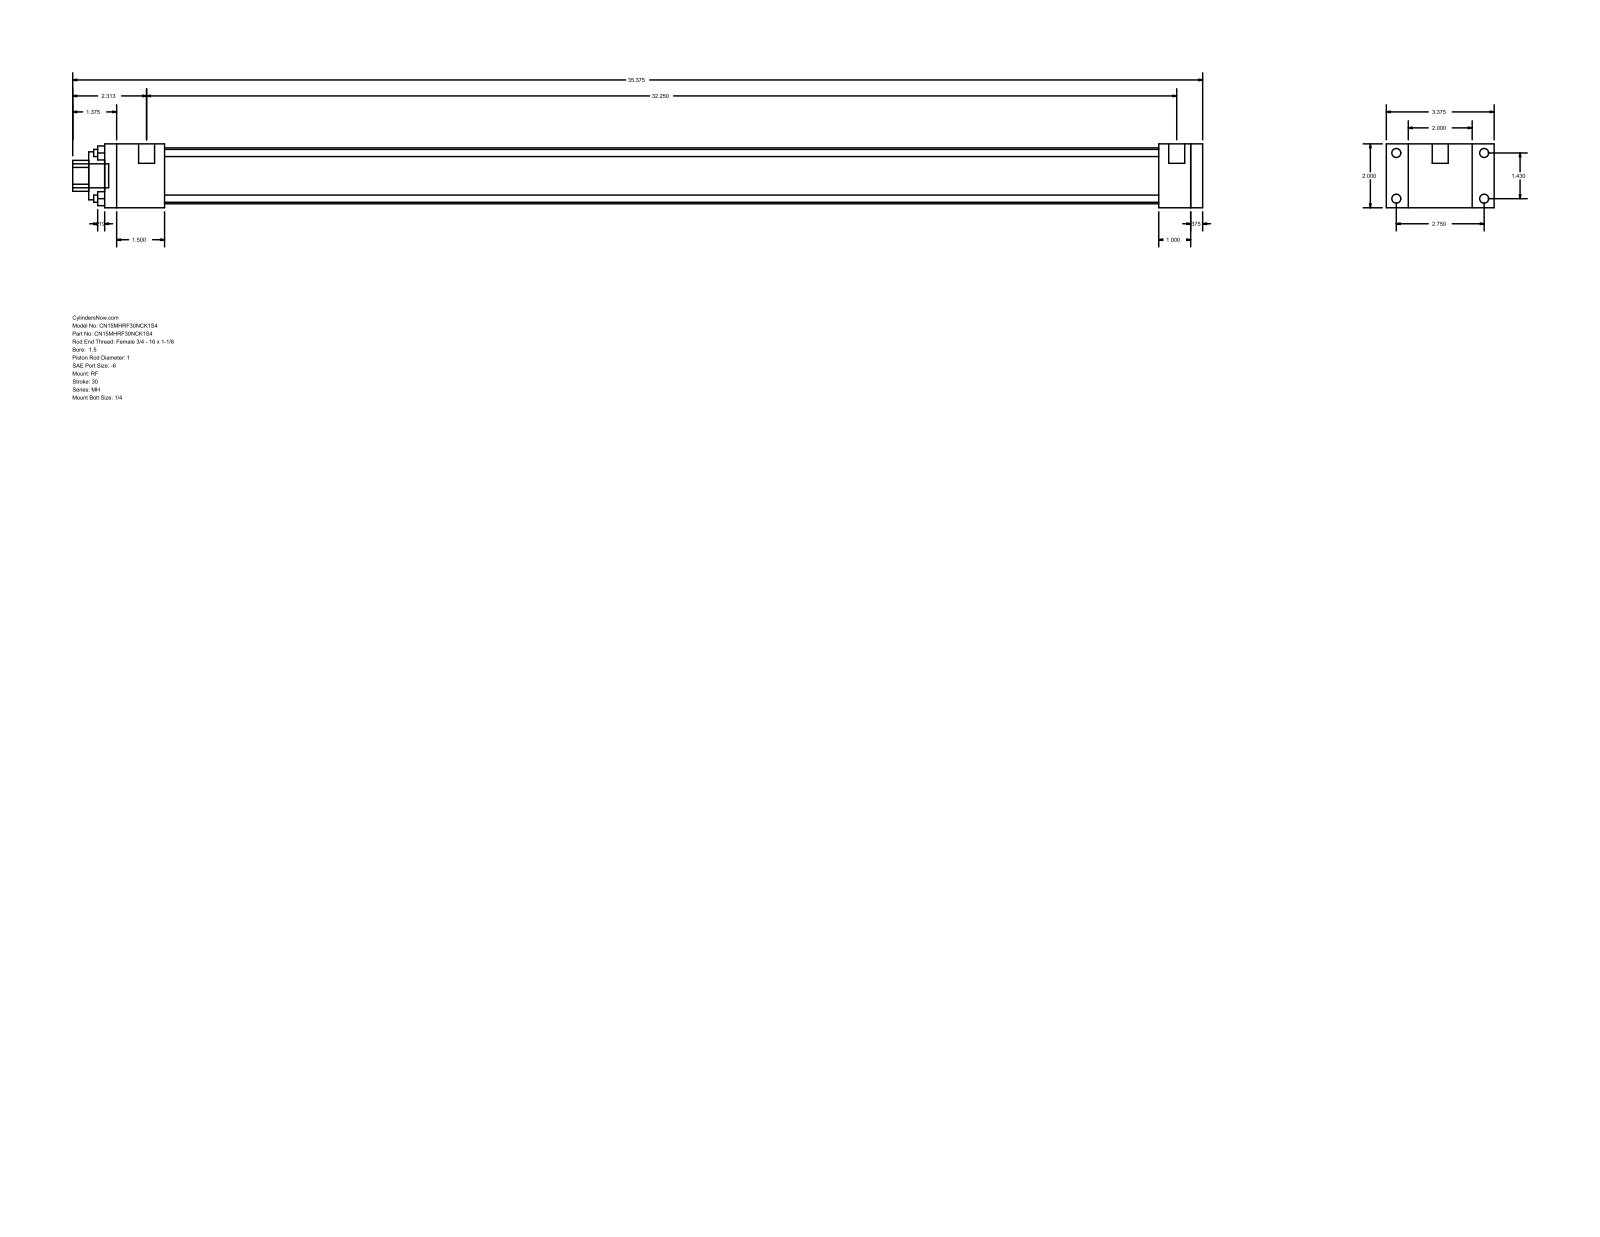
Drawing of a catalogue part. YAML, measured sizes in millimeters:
part_name: "MH_RF__0150_1"
step_written_by: "GSSL Pune (CONFIG_CONTROL_DESIGN)"
units: millimeters
bodies: {solids: 0, faces: 92, planar: 64, cylindrical: 28, other: 0}
overall_size: [898.52, 85.72, 50.8]
round_holes:
  - {diameter: 5.71, count: 4}
  - {diameter: 25.4, count: 1}
  - {diameter: 38.1, count: 1}
  - {diameter: 44.45, count: 1}
round_bosses_or_shafts:
  - {diameter: 7.14, count: 4}
  - {diameter: 5.56, count: 4}
  - {diameter: 12.7, count: 2}
  - {diameter: 19.05, count: 1}
partial_cylinders:
  - {radius: 12.29, count: 1}
face_to_face_distances: [50.8, 9.52, 863.6, 25.4, 873.12, 17.46, 68.26, 838.2, 34.92, 47.63]
hole_center_spacings: [25.68, 36.32, 51.36]
